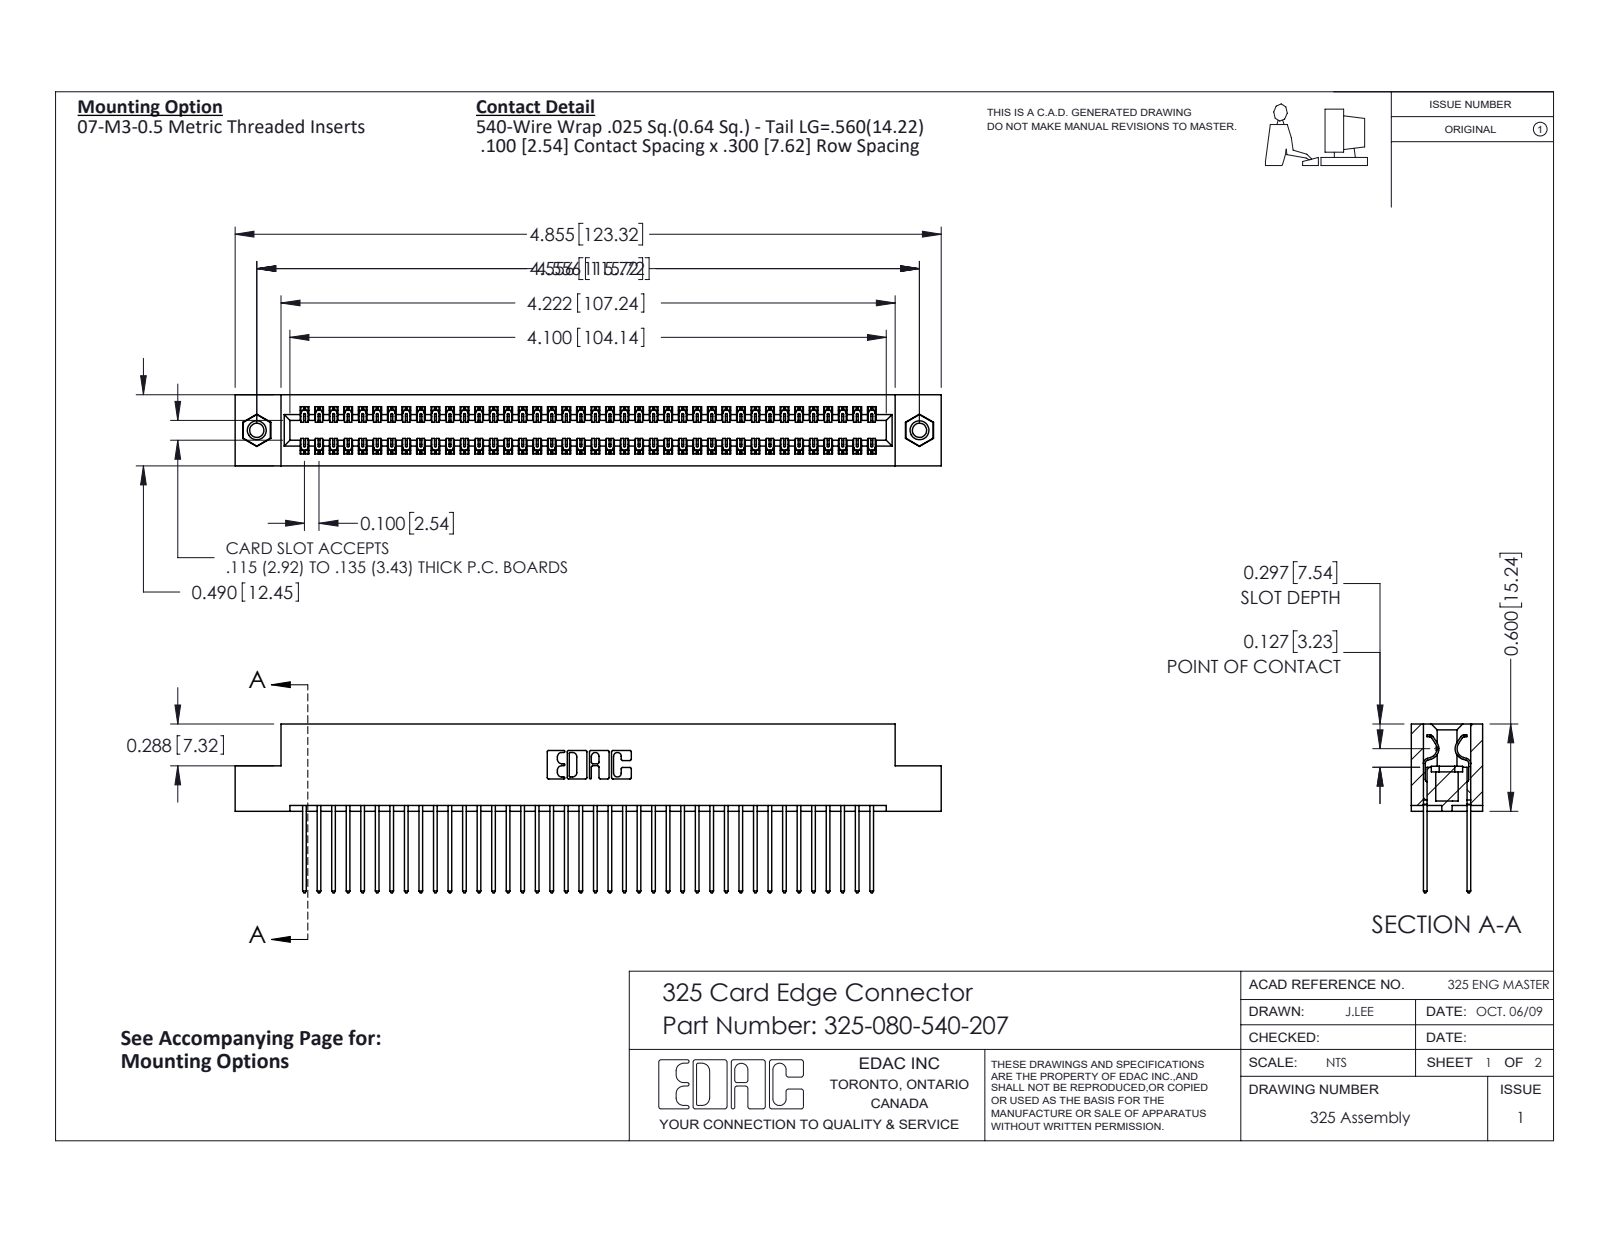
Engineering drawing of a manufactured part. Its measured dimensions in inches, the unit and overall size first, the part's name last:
Units: inches
Overall size (bounding box): 4.855 × 1.16 × 0.49
Round holes (diameter × count): ⌀0.098 ×2, ⌀0.125 ×2, ⌀0.16 ×2
Round bosses / shafts (diameter × count): ⌀0.155 ×2
Partial cylindrical surfaces — rounded edges, fillets, slot ends (radius × count): R0.006 ×120, R0.01 ×80, R0.01 ×22, R0.007 ×6, R0.031 ×6, R0.026 ×3, R0.014 ×2, R0.022 ×2
Main face-to-face distances: 0.083, 0.407, 0.3, 0.107, 0.383, 0.025, 0.49, 0.325, 0.275, 0.56
Hole centre spacings: 4.556
Volume: 0.988 in³ · Surface area: 32.58 in²
Bodies: 83 solids, 4334 faces (2982 planar, 1336 cylindrical, 16 other)
Part name (STEP PRODUCT): 325 Part_TI; 325-080-540-207; 345-250-001_345-250-005-103; 325-292-001_325-293-140
STEP written by: SolidWorks 2016 (CONFIG_CONTROL_DESIGN)
